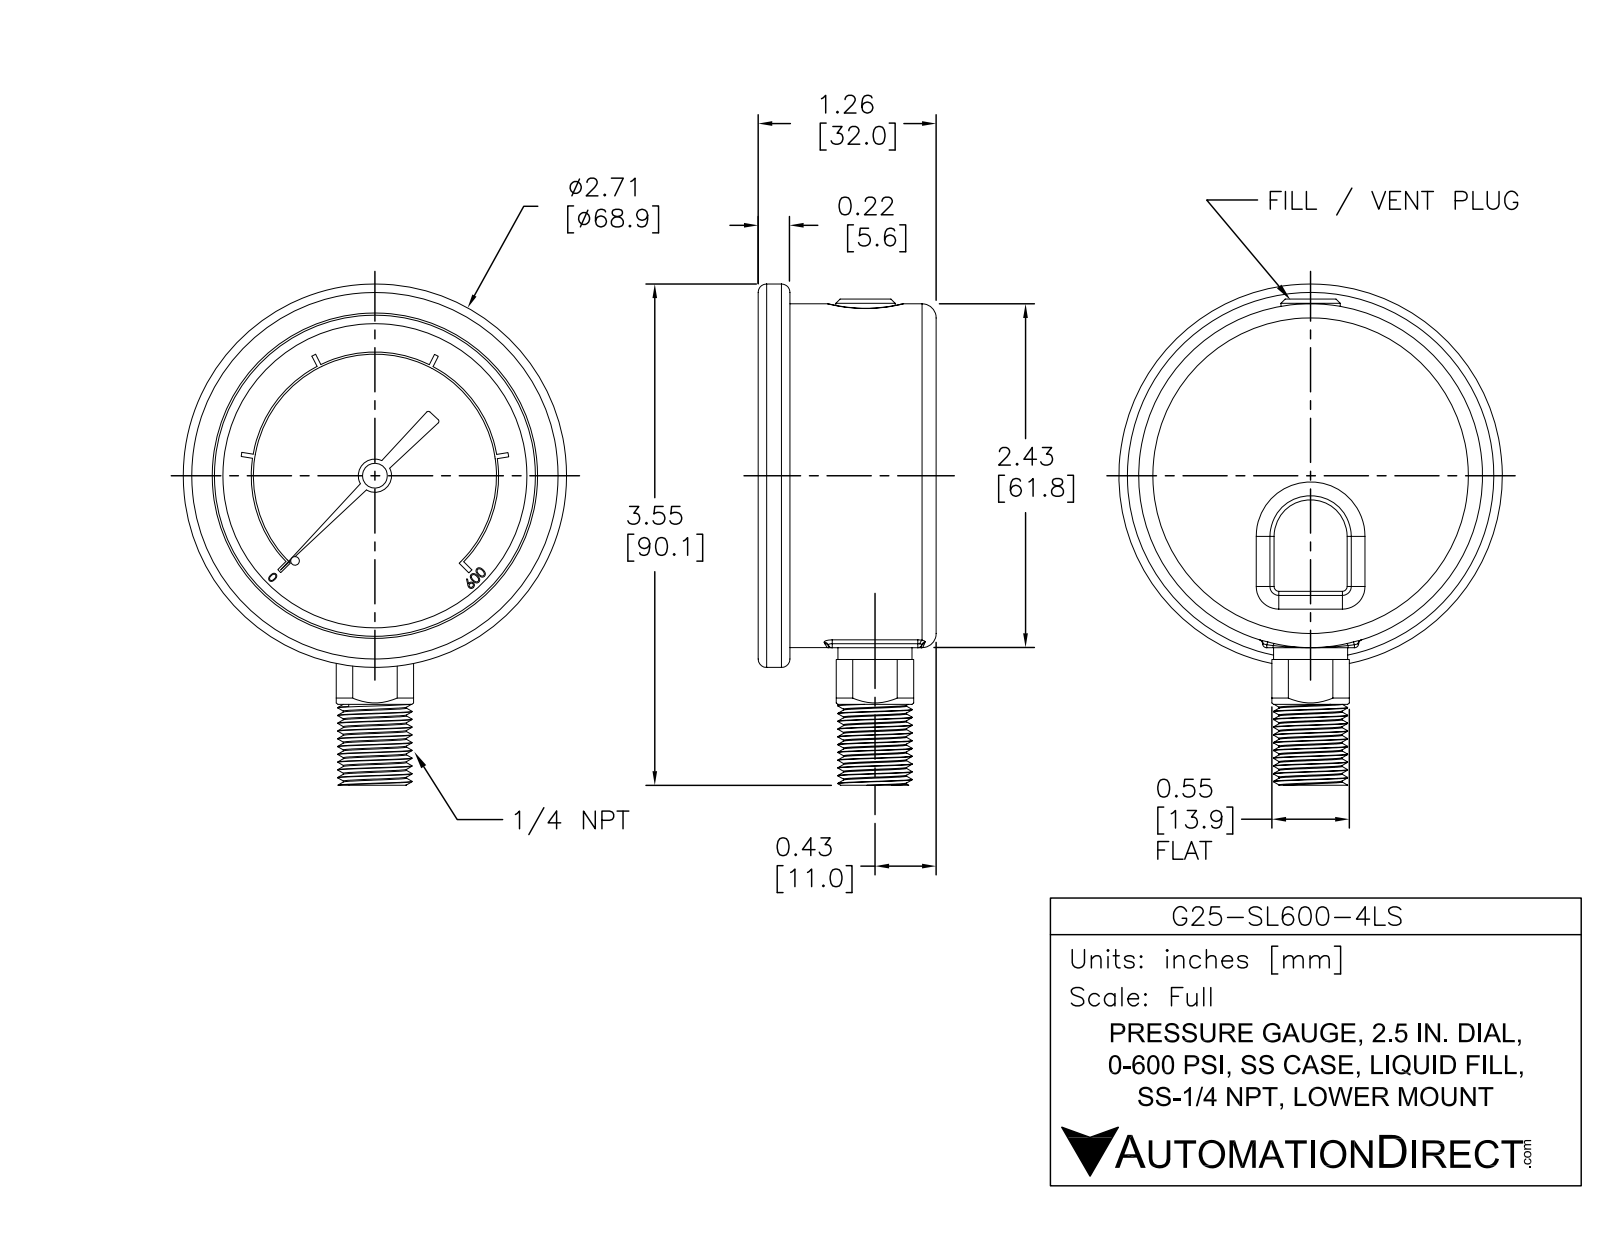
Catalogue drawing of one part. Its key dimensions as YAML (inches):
part_name: "G25-SL600-4LS"
step_written_by: "SolidWorks 2021 (AUTOMOTIVE_DESIGN)"
units: inches
bodies: {solids: 1, faces: 350, planar: 193, cylindrical: 85, other: 72}
overall_size: [3.546, 2.713, 1.26]
volume: 5.273
surface_area: 24.68
round_holes:
  - {diameter: 0.027, count: 1}
  - {diameter: 0.071, count: 1}
  - {diameter: 0.119, count: 1}
  - {diameter: 2.272, count: 1}
round_bosses_or_shafts:
  - {diameter: 2.713, count: 1}
  - {diameter: 2.433, count: 1}
  - {diameter: 0.524, count: 1}
  - {diameter: 0.42, count: 1}
  - {diameter: 0.235, count: 1}
  - {diameter: 0.176, count: 1}
  - {diameter: 0.14, count: 1}
  - {diameter: 0.041, count: 1}
partial_cylinders:
  - {radius: 0.03, count: 9}
  - {radius: 0.1, count: 3}
  - {radius: 0.015, count: 2}
  - {radius: 0.316, count: 1}
  - {radius: 0.86, count: 1}
  - {radius: 0.875, count: 1}
face_to_face_distances: [1.01, 1.26, 0.25, 1.035, 0.025, 0.225, 0.1, 0.91, 0.935, 1.16]
hole_center_spacings: [0.067]
